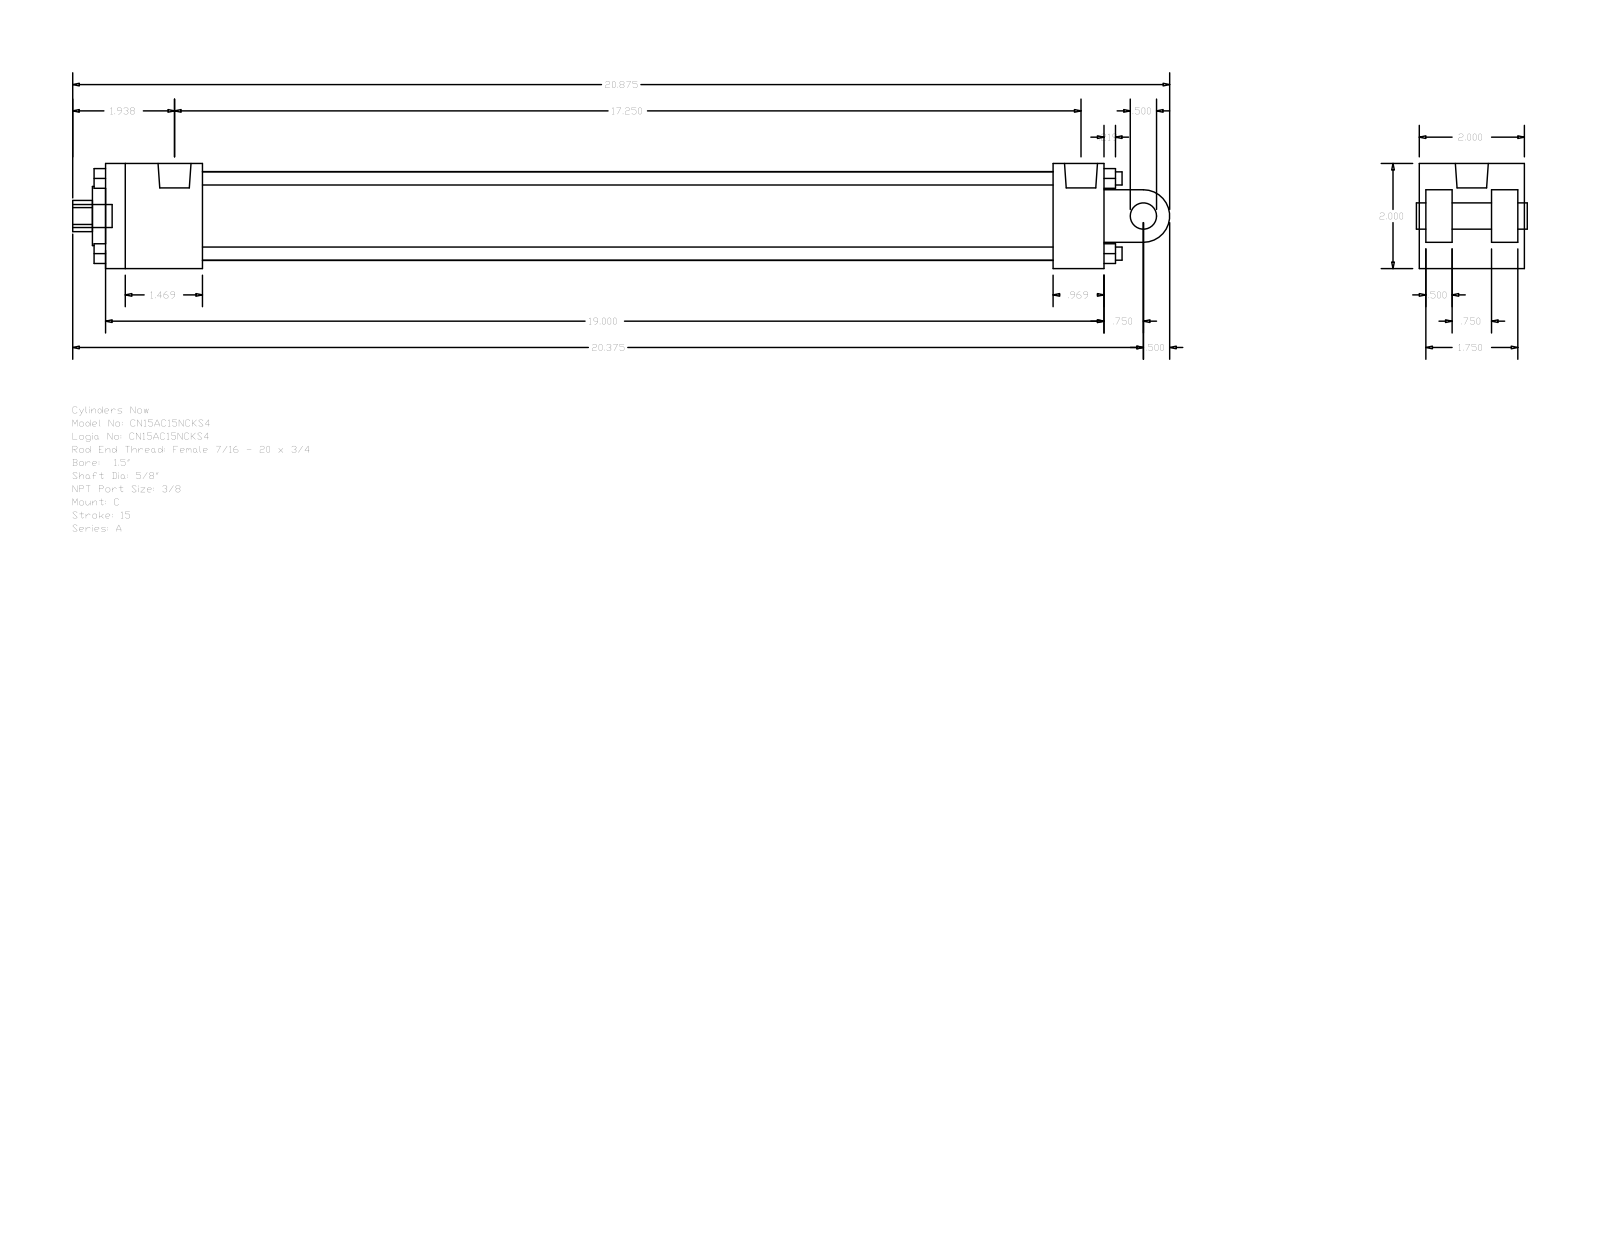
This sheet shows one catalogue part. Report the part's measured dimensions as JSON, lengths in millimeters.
{"part_name": "A_C__0150_0.625", "step_written_by": "GSSL Pune (CONFIG_CONTROL_DESIGN)", "units": "millimeters", "bodies": {"solids": 0, "faces": 135, "planar": 102, "cylindrical": 33, "other": 0}, "overall_size": [530.23, 50.8, 50.8], "round_holes": [[5.56, 2], [15.88, 1], [15.93, 1], [28.57, 1], [42.93, 1]], "round_bosses_or_shafts": [[6.35, 4], [5.56, 2], [15.93, 1], [12.7, 1], [11.11, 1]], "partial_cylinders_radius": [[7.54, 1], [12.7, 1]], "face_to_face_distances": [50.8, 12.7, 482.6, 3.17, 15.87, 34.93, 47.63, 31.76, 457.99, 24.61], "hole_center_spacings": [3.97]}
